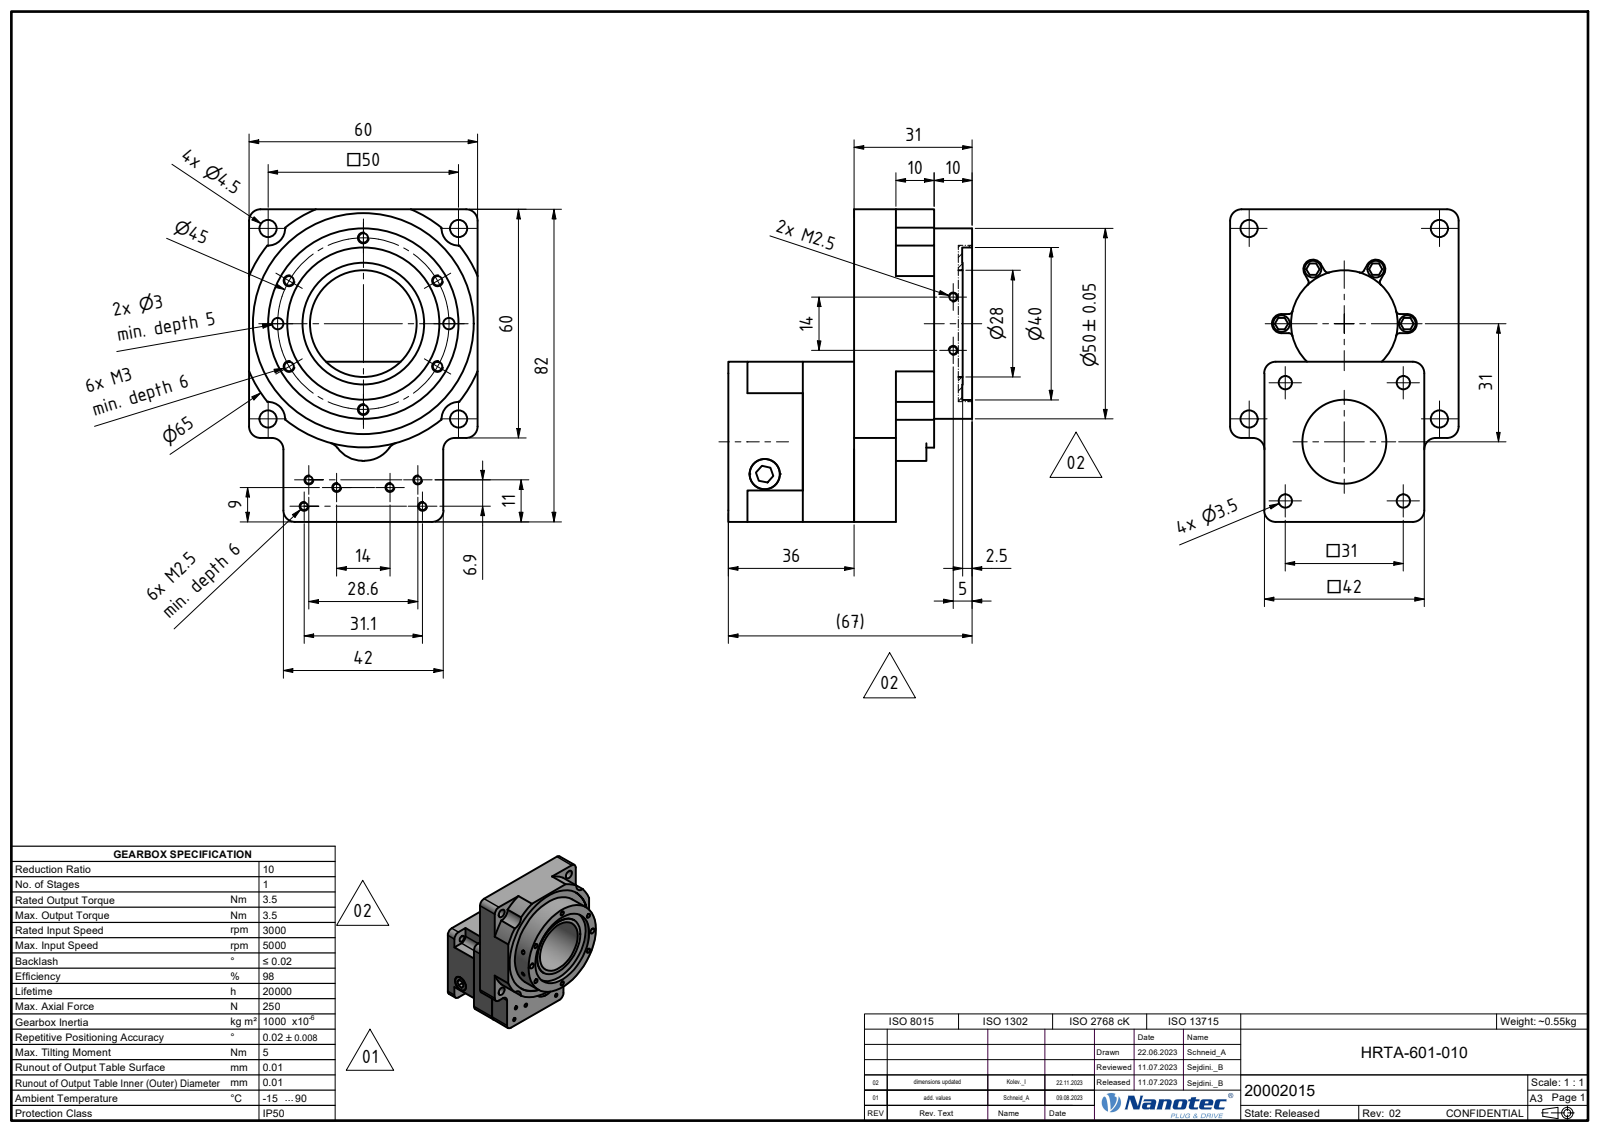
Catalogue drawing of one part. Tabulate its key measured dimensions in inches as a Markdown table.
| quantity | value |
| --- | --- |
| part name | D-00005328 |
| STEP written by | Autodesk Inventor 2021 (AUTOMOTIVE_DESIGN) |
| units | inches |
| bodies | 3 solids, 231 faces (121 planar, 94 cylindrical, 16 other) |
| overall size | 3.228 × 2.52 × 2.362 |
| volume | 8.369 in³ |
| surface area | 51.91 in² |
| round holes (diameter × count) | 0.079 × 8, 0.097 × 6, 0.138 × 4, 0.177 × 4, 0.118 × 2, 0.315 × 2, 0.866 × 1, 1.102 × 1, 1.575 × 1, 2.283 × 1 |
| round bosses / shafts (diameter × count) | 0.173 × 6, 1.969 × 1, 1.26 × 1, 1.22 × 1, 0.314 × 1 |
| partial cylindrical surfaces (radius × count) | 0.118 × 16, 0.039 × 12, 0.098 × 6, 0.177 × 4, 0.315 × 2, 1.28 × 1 |
| main face-to-face distances | 0.413, 0.354, 1.654, 0.886, 2.008, 1.299, 2.362, 1.24, 0.433, 1.732 |
| hole center spacings | 0.886, 0.989, 2.113, 0.863, 1.22, 0.459, 0.583, 0.67 |
